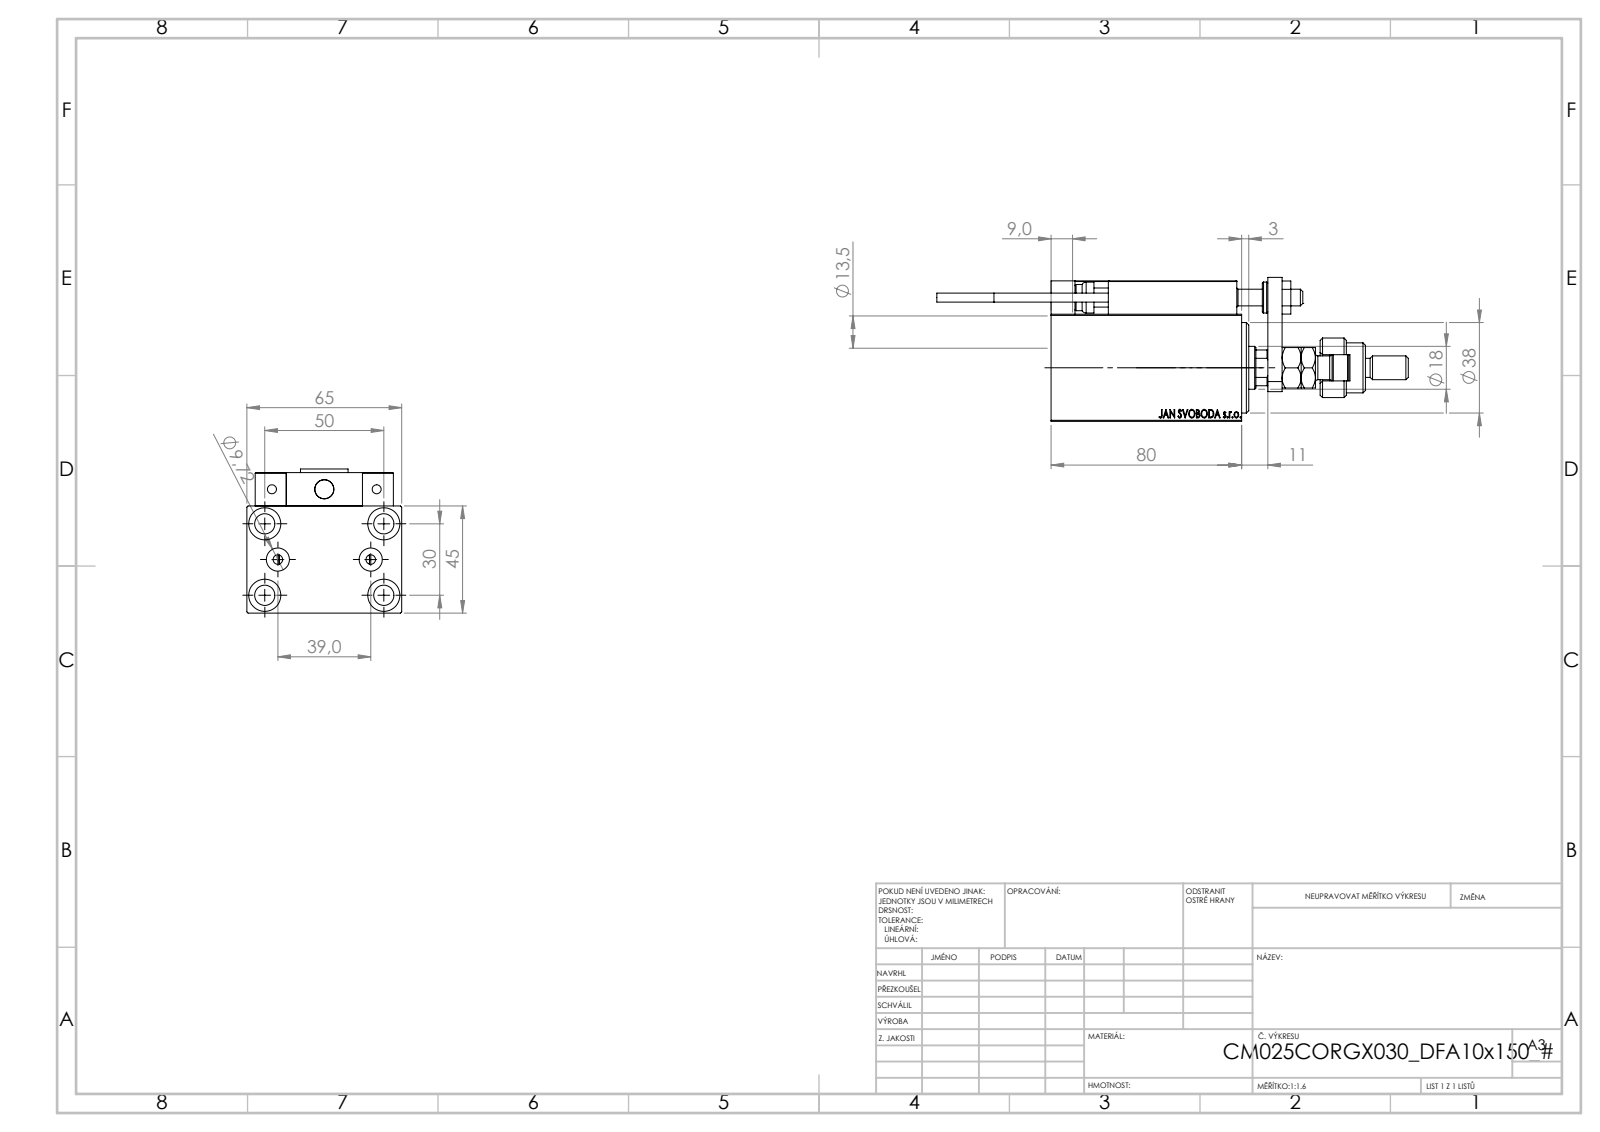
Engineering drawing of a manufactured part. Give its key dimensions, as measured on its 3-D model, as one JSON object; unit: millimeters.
{"part_name": "SWITCH_X_FRONT_BACK; NUT_D12; V450CM_C_Body; MAGNET (+8 more)", "step_written_by": "SolidWorks 2019 (CONFIG_CONTROL_DESIGN)", "units": "millimeters", "bodies": {"solids": 25, "faces": 1363, "planar": 588, "cylindrical": 197, "other": 578}, "overall_size": [198, 65, 60.5], "volume_mm3": 260650, "surface_area_mm2": 80515, "round_holes": [[4, 6], [8, 5], [8.5, 5], [3.2, 4], [13.5, 4], [5, 2], [9.72, 2], [7, 1], [14.5, 1], [18, 1], [21.5, 1], [27, 1]], "round_bosses_or_shafts": [[5, 2], [3.8, 2], [25, 1], [21, 1], [16, 1], [13, 1], [11, 1], [10, 1]], "partial_cylinders_radius": [[0.3, 30], [3, 2], [5.5, 1], [8.5, 1], [8.75, 1]], "face_to_face_distances": [45, 65, 14, 59, 6, 3, 7, 91, 19, 13], "hole_center_spacings": [15.98, 29.15, 46.96, 11.37, 19.5, 20, 28.9, 29.59]}
